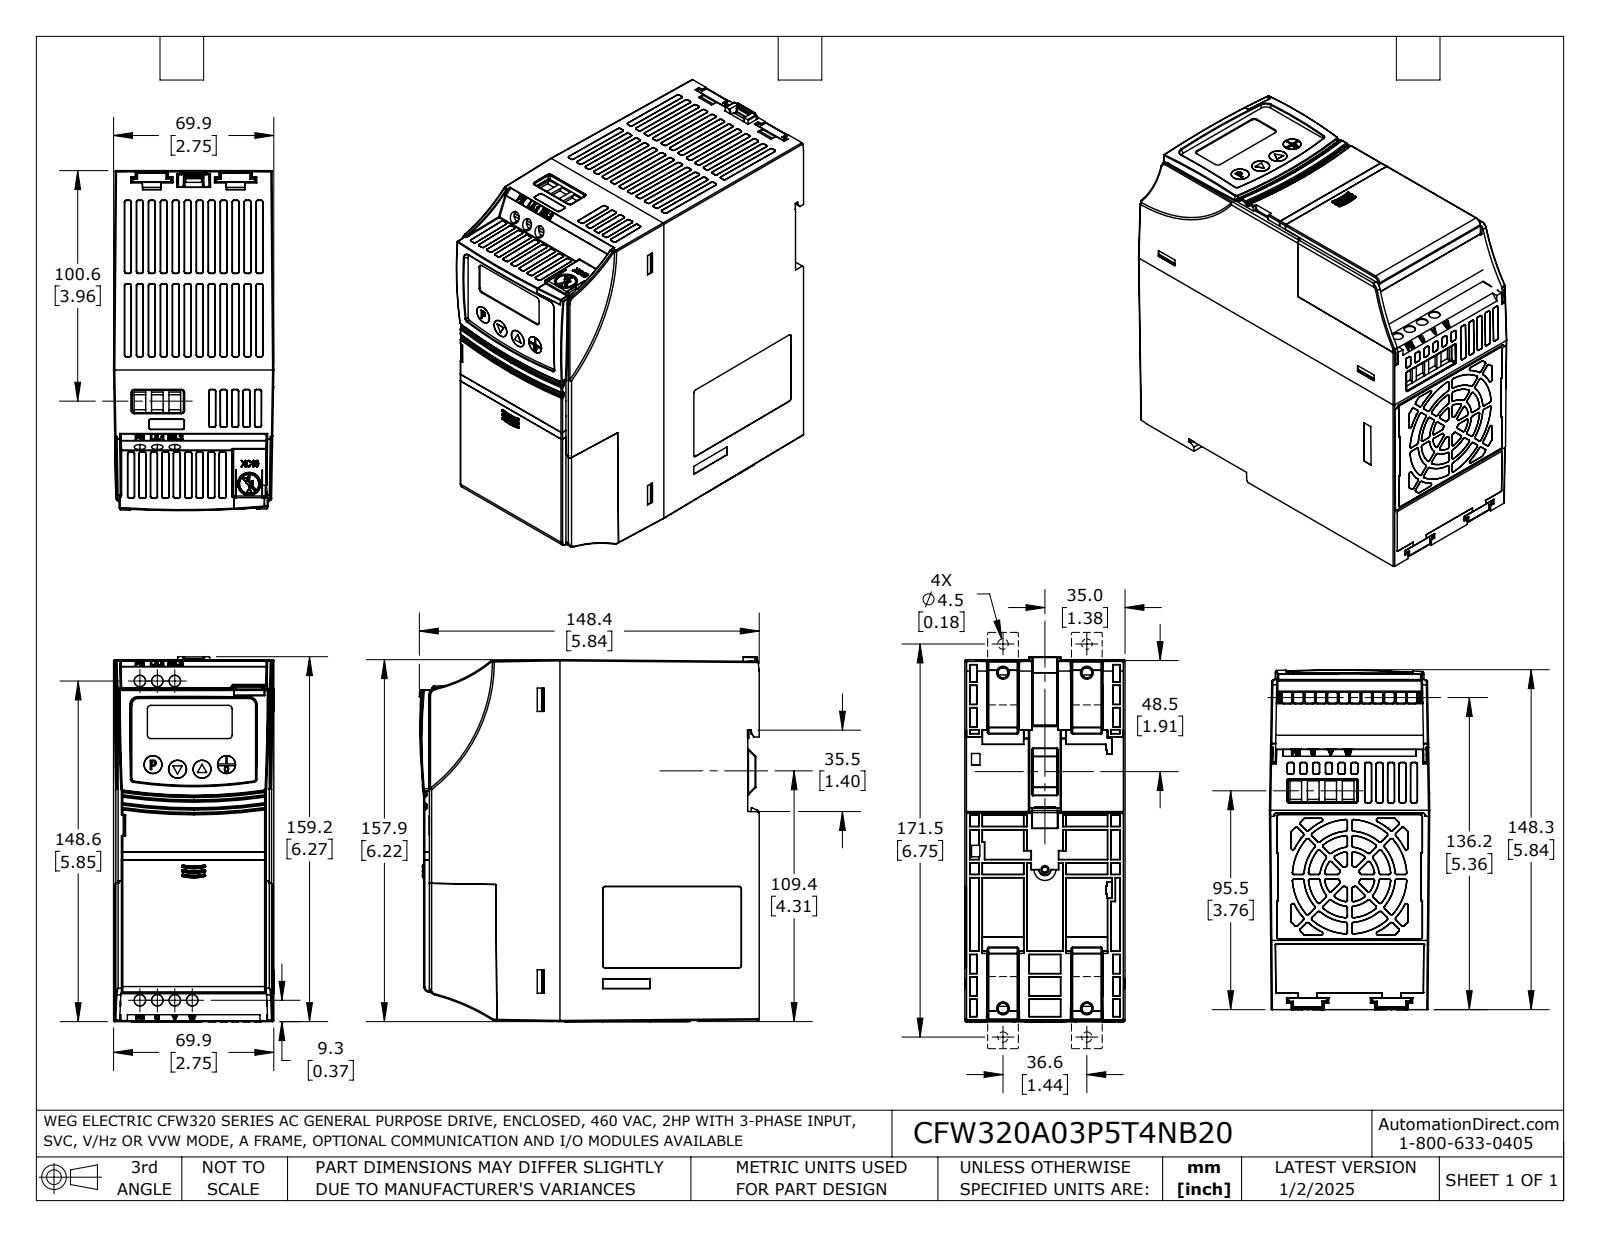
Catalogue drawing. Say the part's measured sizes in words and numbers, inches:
The part is named "CFW320A03P5T4NB20". Its 3-D file was written by "SolidWorks 2021 (AUTOMOTIVE_DESIGN)". It is 6 solids with 3715 faces: 1587 planar, 853 cylindrical and 1275 other. Overall it measures 6.269 by 5.841 by 2.754 inches. Its volume is 15.24 cubic inches and its surface area 309 square inches. Round holes: 3 of diameter 0.197. Partial cylindrical surfaces (rounded edges, fillets, slot ends): 327 of radius 0.012, 150 of radius 0.02, 13 of radius 0.039, 5 of radius 0.03, 3 of radius 0.118, 2 of radius 0.01, 1 of radius 0.098, 1 of radius 0.126. The main face-to-face distances are 0.07, 0.055, 0.019, 0.05, 6, 5.33, 5.275, 5.571, 5.516, 0.241. The hole center spacings are 0.3, 0.6.
